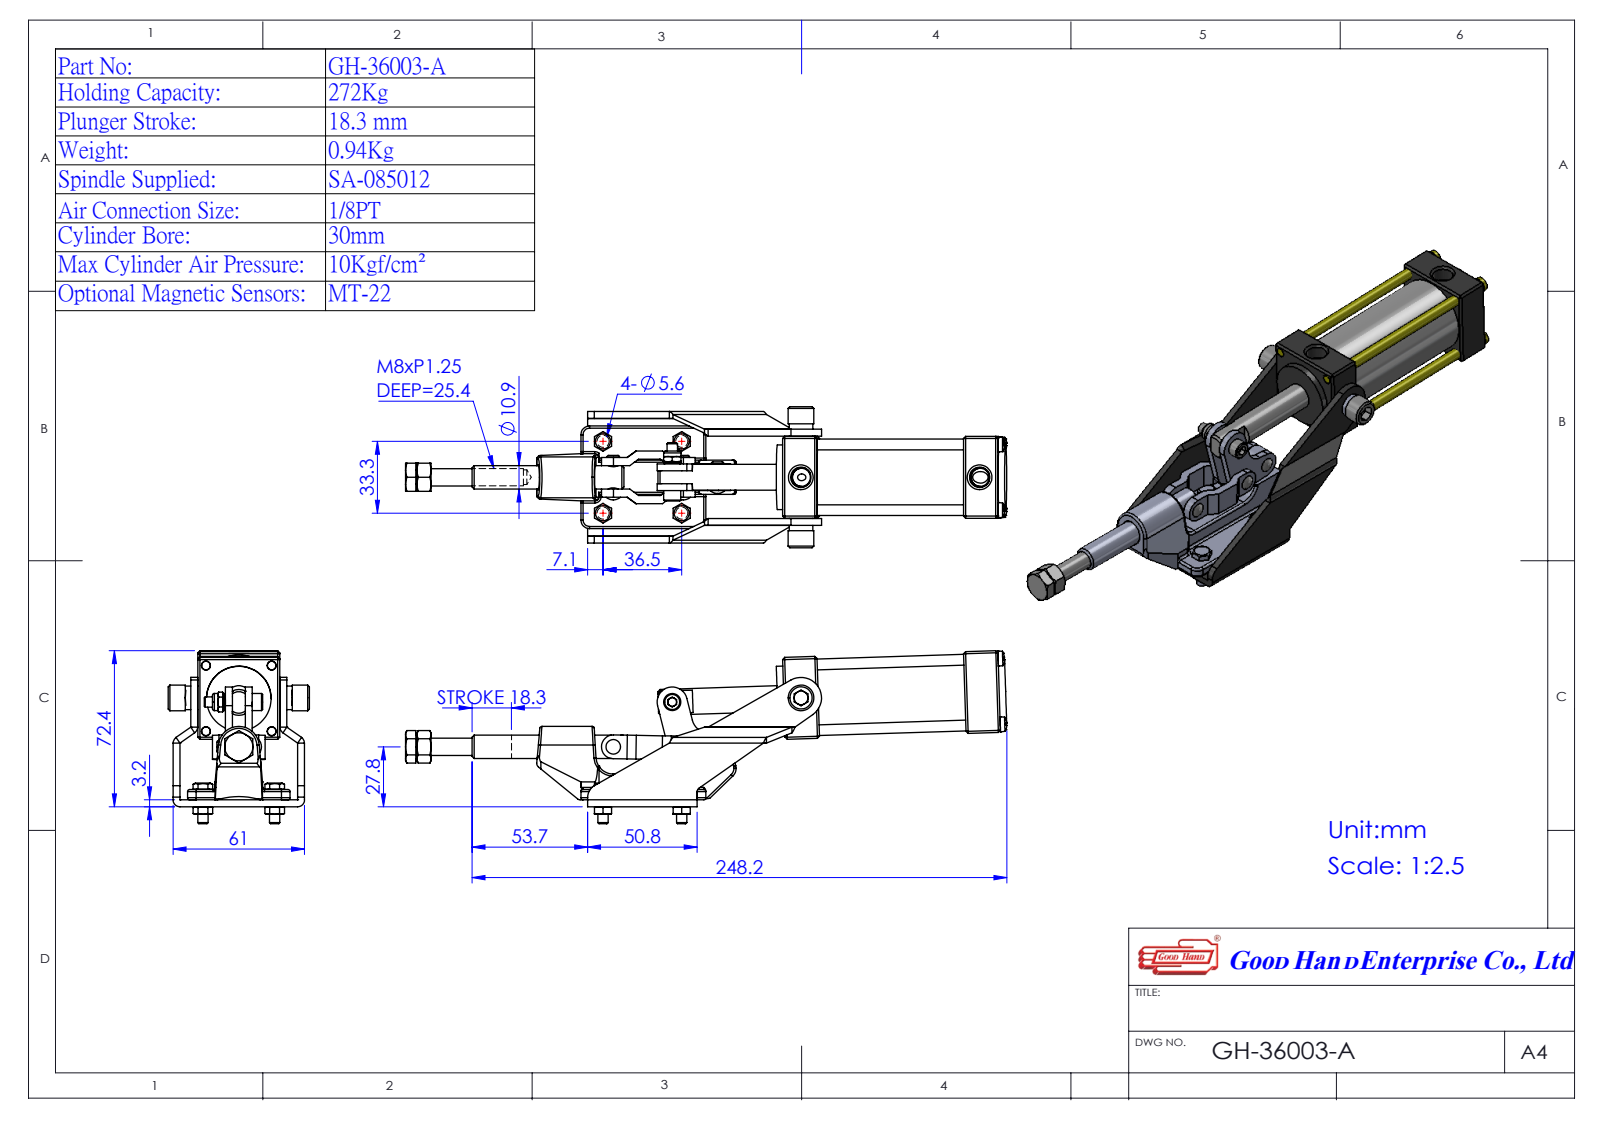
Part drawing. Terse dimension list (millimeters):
name: Group2^GH-36003-A(簡化)-1; Group7^GH-36003-A(簡化)-1; Group8^GH-36003-A(簡化)-1; Group5^GH-36003-A(簡化)-1 (+4 more)
written by: SolidWorks 2016 (AUTOMOTIVE_DESIGN)
unit: mm
bodies: 8 solids, 732 faces (403 planar, 185 cylindrical, 144 other)
size: 279 × 80.29 × 65.47
volume: 175 271 mm³; area: 77 613 mm²
holes: 4× ⌀4, 2× ⌀7.9, 1× ⌀4.2, 1× ⌀4.7, 1× ⌀4.8, 1× ⌀5, 1× ⌀5.86, 1× ⌀6, 1× ⌀6.8, 1× ⌀10.9, 1× ⌀12, 1× ⌀30
bosses: 4× ⌀7, 4× ⌀6, 4× ⌀5, 4× ⌀4.76, 3× ⌀30, 3× ⌀5.83, 2× ⌀8, 1× ⌀35
rounds: 7× R2, 6× R3.21, 4× R4, 3× R8, 2× R5.5, 2× R6, 2× R7, 2× R9.5
face distances: 3.2, 24.3, 33.5, 8.2, 49.6, 57.8, 16.1, 25.3, 11.5, 4.8
hole spacings: 15.91, 21.95, 29.56, 32.49, 34.36, 44.91, 48.39, 59.39
